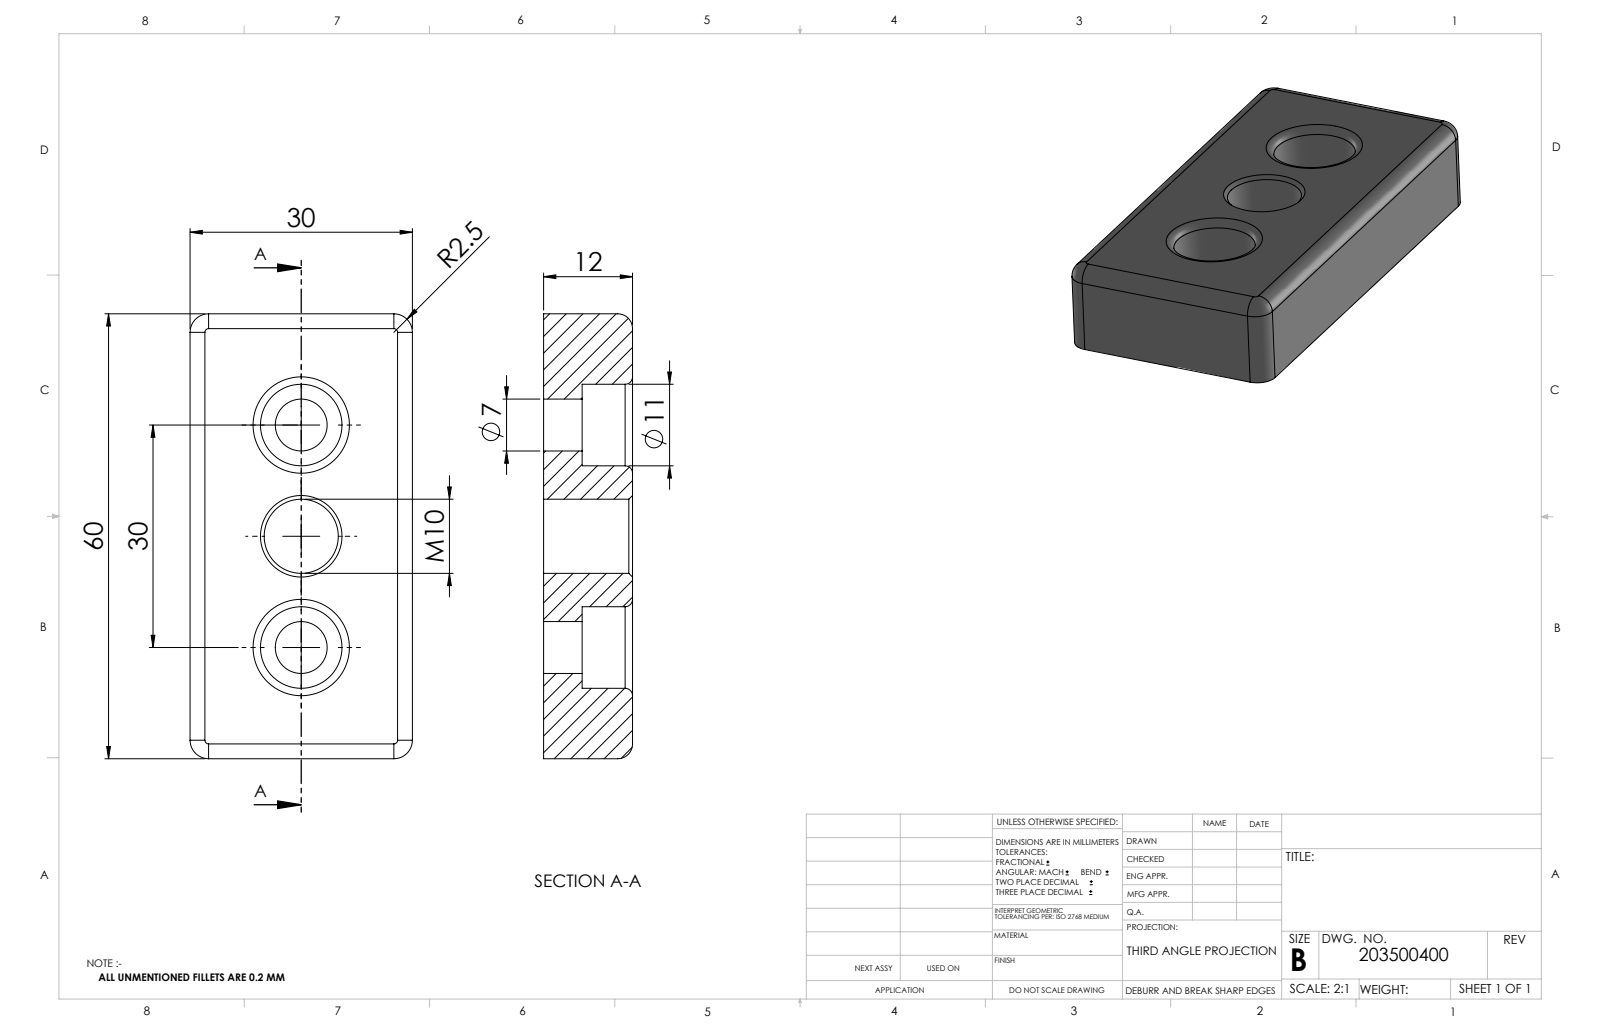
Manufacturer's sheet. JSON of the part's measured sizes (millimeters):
{"part_name": "203500400_c_1", "step_written_by": "SolidWorks 2014 (CONFIG_CONTROL_DESIGN)", "units": "millimeters", "bodies": {"solids": 1, "faces": 36, "planar": 8, "cylindrical": 18, "other": 10}, "overall_size": [60, 30, 12], "volume_mm3": 18733, "surface_area_mm2": 6272, "round_holes": [[7, 2], [11, 2], [10, 1]], "partial_cylinders_radius": [[2, 4], [2.5, 4]], "face_to_face_distances": [12, 30, 60, 5.2, 6.8], "hole_center_spacings": [15, 30]}
